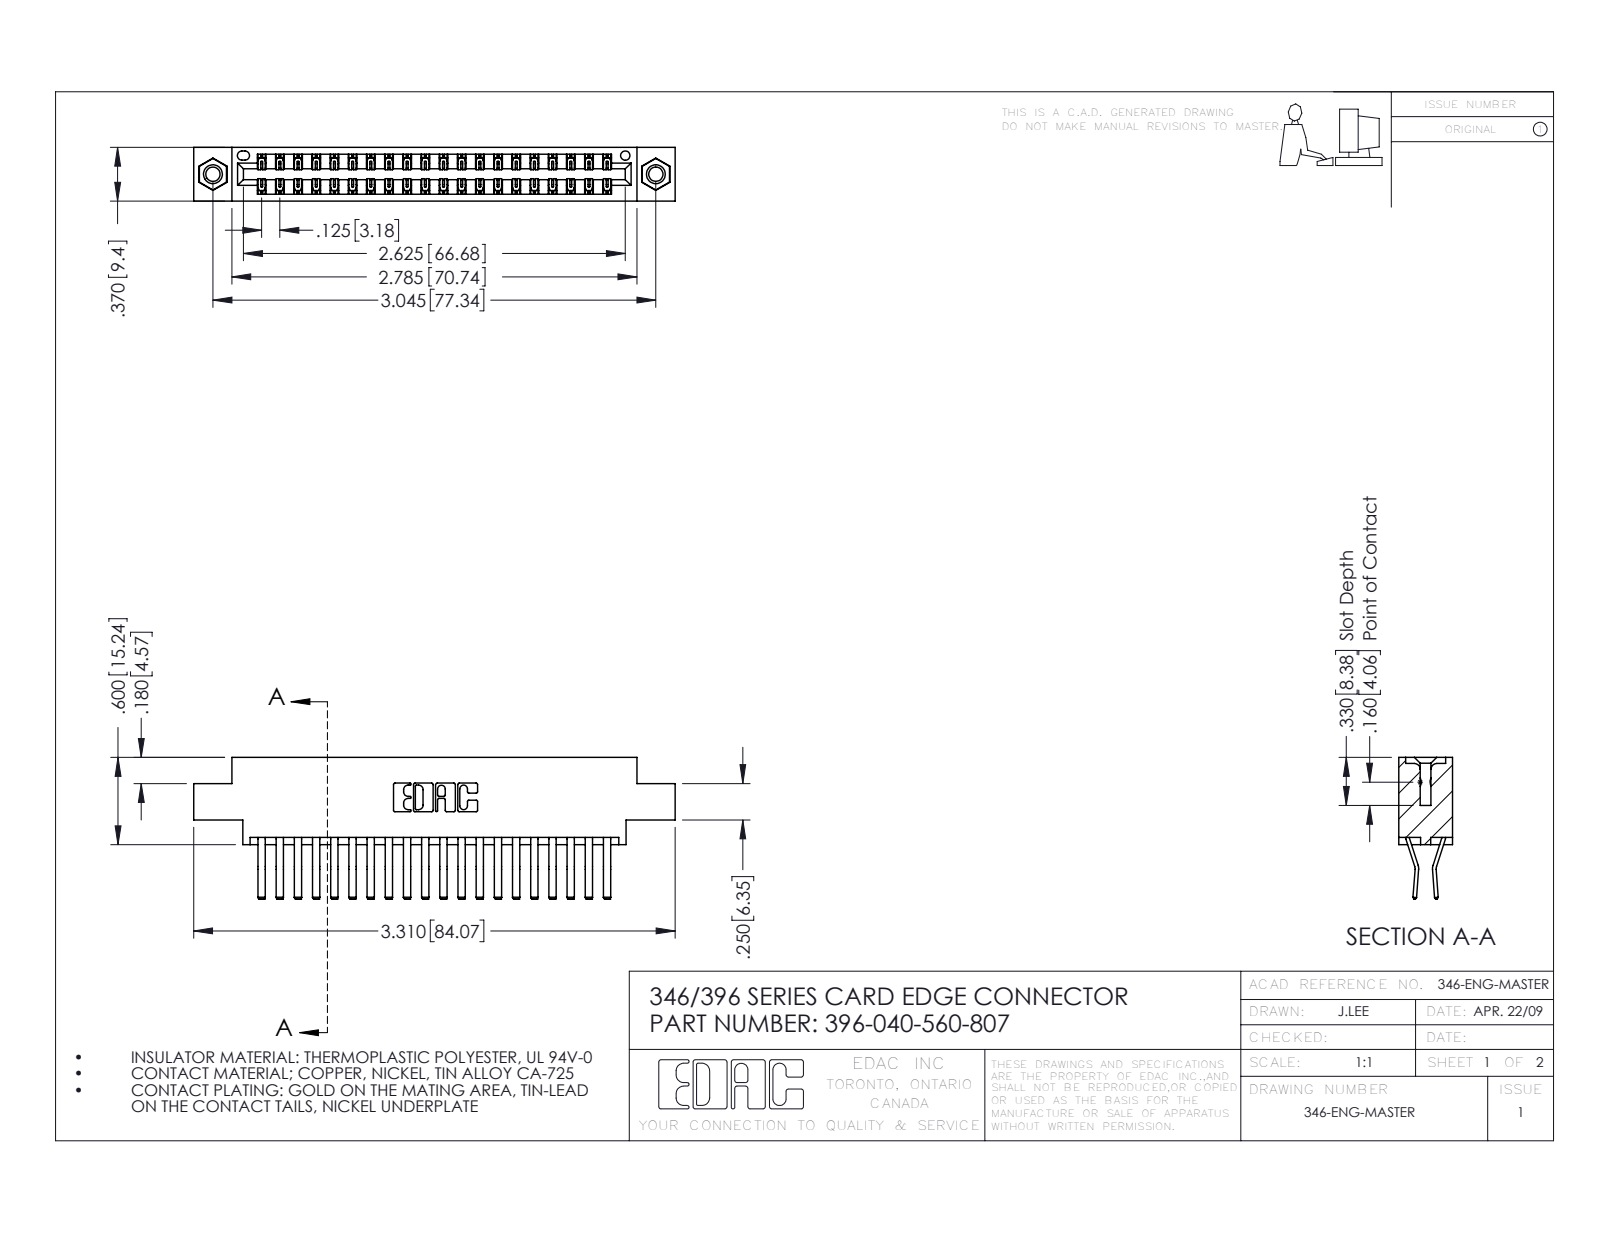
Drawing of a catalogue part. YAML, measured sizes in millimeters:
part_name: "345-250-001_345-250-005-103; 396-040-560-807; 345-292-001_560 Tail; 346 Part_0.170 Offset - 0.156 Dia-TI"
step_written_by: "SolidWorks 2016 (CONFIG_CONTROL_DESIGN)"
units: millimeters
bodies: {solids: 43, faces: 2346, planar: 1512, cylindrical: 818, other: 16}
overall_size: [84.1, 24.8, 9.4]
volume: 8130
surface_area: 11730
round_holes:
  - {diameter: 2.5, count: 2}
  - {diameter: 3.2, count: 2}
  - {diameter: 4, count: 2}
  - {diameter: 1.6, count: 1}
round_bosses_or_shafts:
  - {diameter: 3.9, count: 2}
partial_cylinders:
  - {radius: 0.2, count: 60}
  - {radius: 0.3, count: 22}
  - {radius: 0.2, count: 6}
  - {radius: 0.8, count: 6}
  - {radius: 0.7, count: 3}
  - {radius: 0.3, count: 2}
  - {radius: 0.4, count: 2}
  - {radius: 0.6, count: 2}
face_to_face_distances: [1.2, 8.2, 9.4, 6.4, 0.6, 1.8, 7.6, 7, 5.6, 3.8]
hole_center_spacings: [6.2, 72.1, 77.3]
